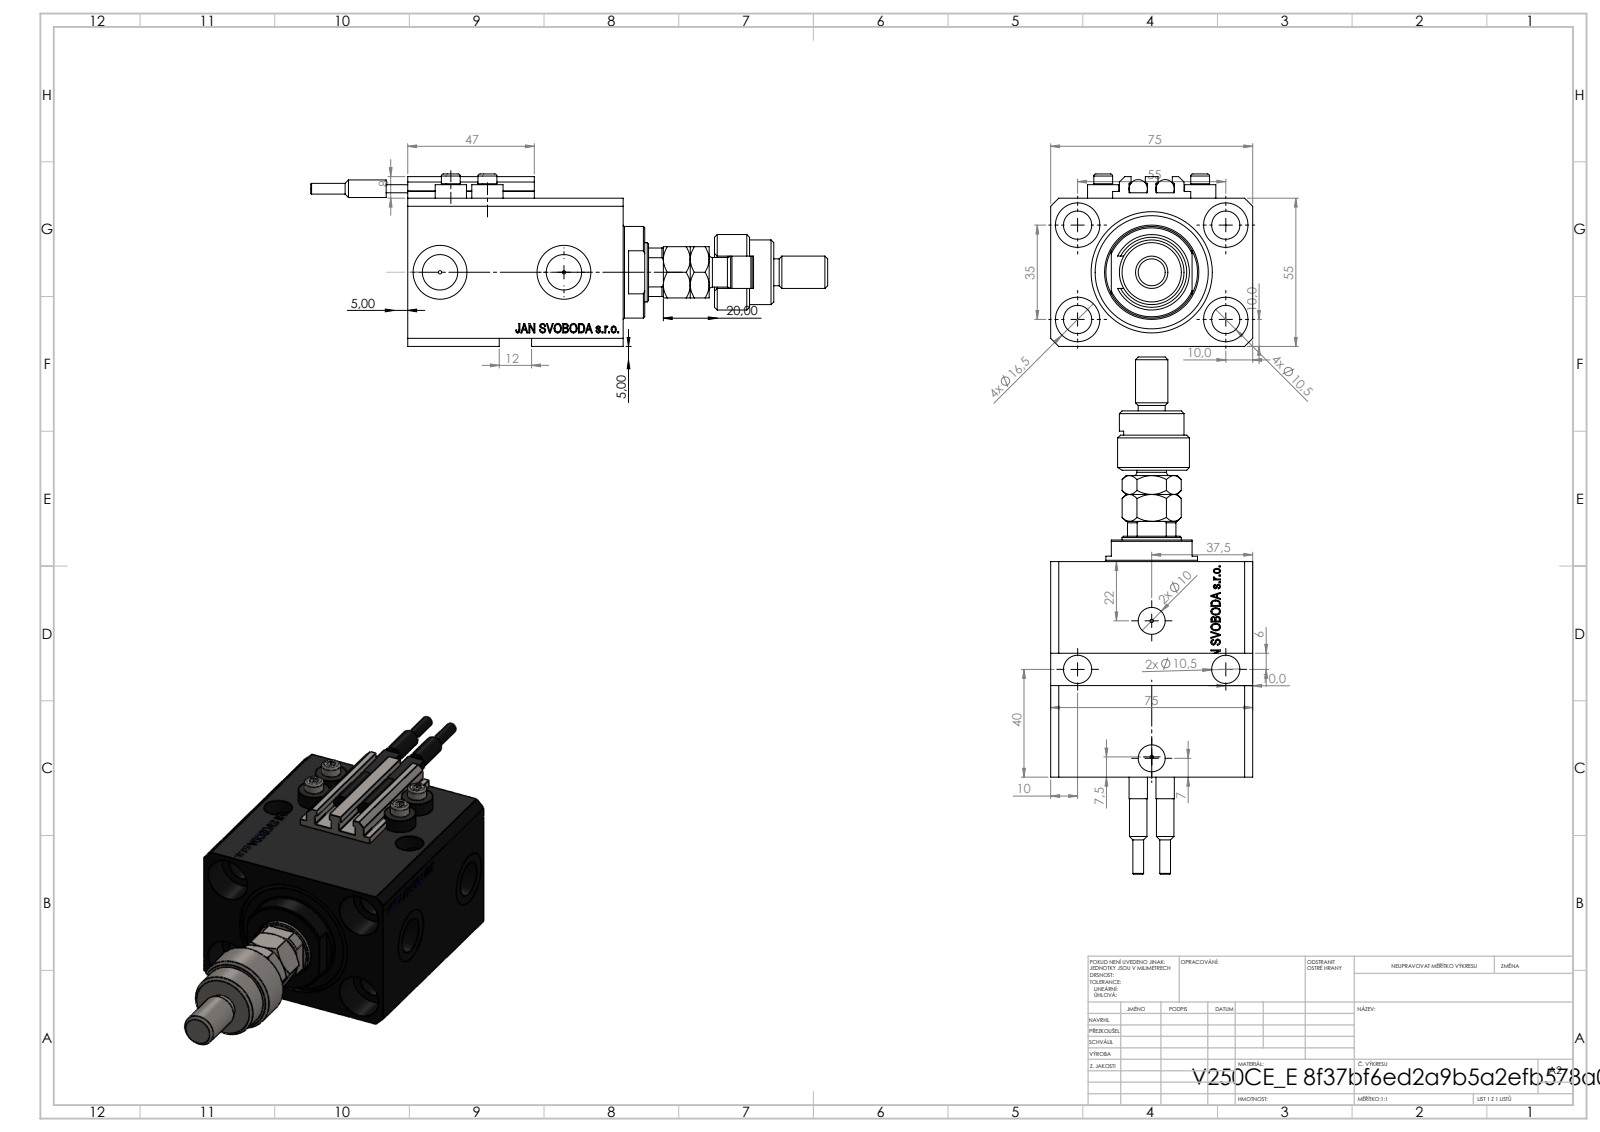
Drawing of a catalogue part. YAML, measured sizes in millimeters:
part_name: "SWITCH_V250CE; MFA; ALLEN BOLT V250CE; V250CE_VC_E (+3 more)"
step_written_by: "SolidWorks 2019 (CONFIG_CONTROL_DESIGN)"
units: millimeters
bodies: {solids: 11, faces: 335, planar: 146, cylindrical: 67, other: 122}
overall_size: [192, 59, 45]
volume: 94773
surface_area: 32026
round_holes:
  - {diameter: 10.5, count: 1}
  - {diameter: 22, count: 1}
round_bosses_or_shafts:
  - {diameter: 4, count: 6}
  - {diameter: 7, count: 4}
  - {diameter: 6.8, count: 2}
  - {diameter: 6.5, count: 2}
  - {diameter: 45, count: 1}
  - {diameter: 34, count: 1}
  - {diameter: 32, count: 1}
  - {diameter: 28, count: 1}
partial_cylinders:
  - {radius: 0.2, count: 10}
  - {radius: 9.75, count: 1}
  - {radius: 10.5, count: 1}
face_to_face_distances: [8, 2, 3, 15, 55.1, 6, 0.5, 19, 48, 20]
